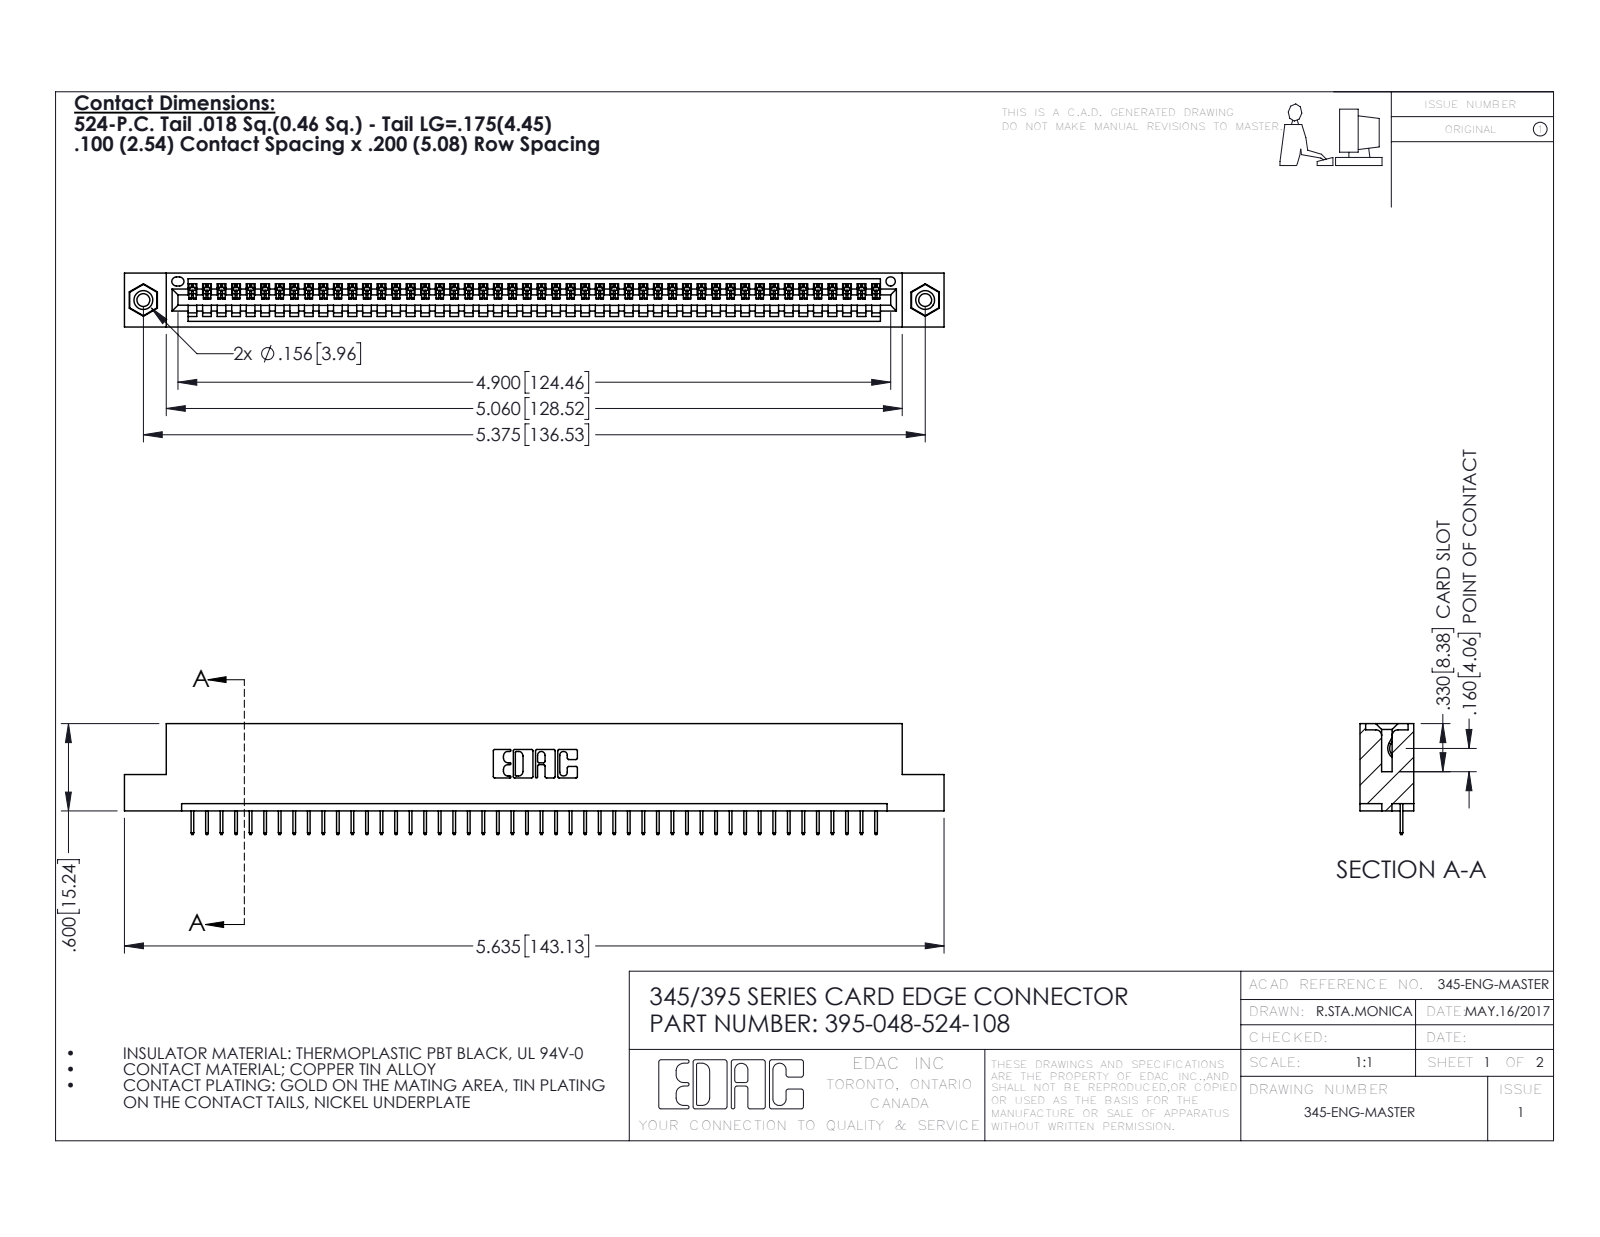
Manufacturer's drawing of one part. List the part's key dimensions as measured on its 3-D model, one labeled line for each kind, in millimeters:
Part name (STEP PRODUCT): 395-048-524-108; 345-292-001_345-293-124; 345-250-001_345-250-003-102; 345 Part_Flush Mounting Lugs - 0.156 Dia-TI
STEP written by: SolidWorks 2016 (CONFIG_CONTROL_DESIGN)
Units: millimetres
Bodies: 51 solids, 3162 faces (2320 planar, 826 cylindrical, 16 other)
Overall size (bounding box): 143.1 × 19.4 × 9.4
Volume: 13 500 mm³ · Surface area: 17 370 mm²
Round holes (diameter × count): ⌀2.3 ×2, ⌀3.2 ×2, ⌀4 ×2, ⌀1.6 ×1
Round bosses / shafts (diameter × count): ⌀3.9 ×2
Partial cylindrical surfaces — rounded edges, fillets, slot ends (radius × count): R0.2 ×96, R0.3 ×22, R0.2 ×6, R0.8 ×6, R0.7 ×3, R0.8 ×2, R1 ×2, R0.4 ×1
Main face-to-face distances: 1.8, 7.6, 9.4, 5.1, 2.5, 6.9, 0.6, 5.7, 1.8, 3.8
Hole centre spacings: 6.9, 130.5, 136.5
